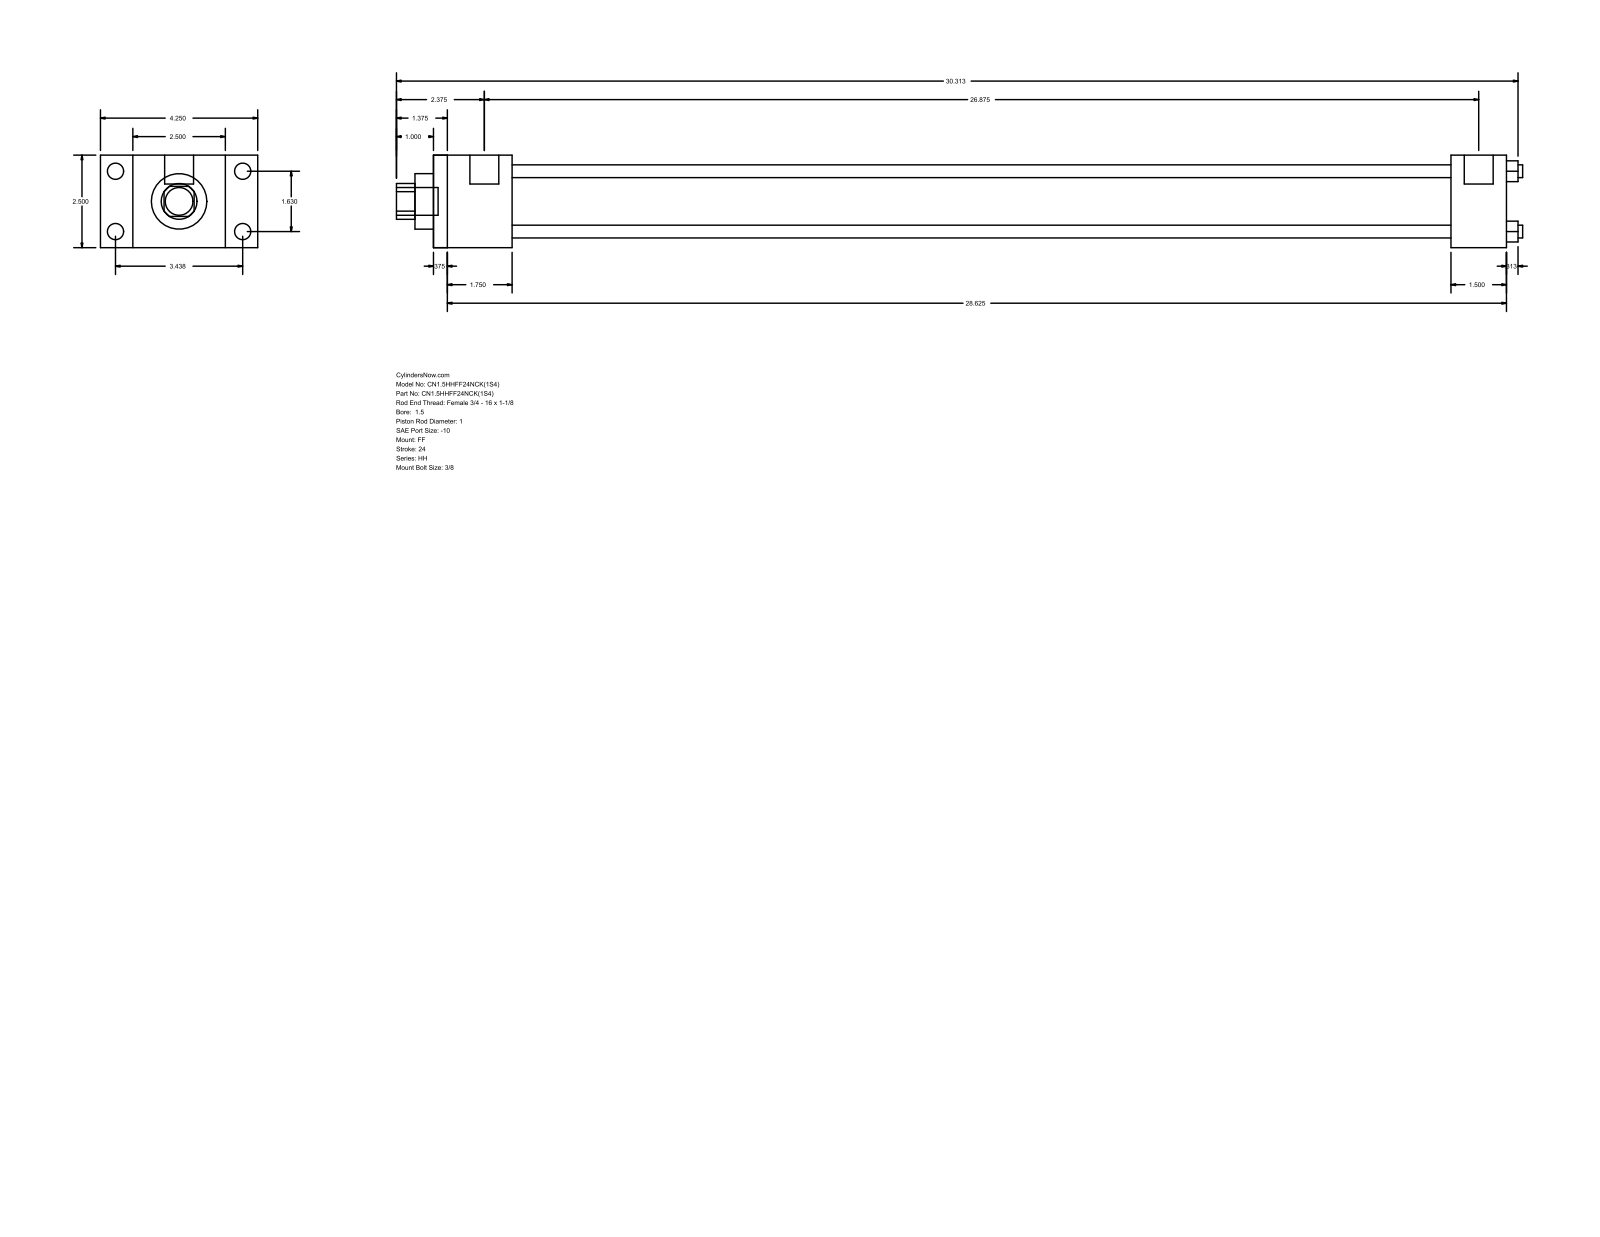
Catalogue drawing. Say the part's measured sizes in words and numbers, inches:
The part is named "HH_FF__0150_1". Its 3-D file was written by "GSSL Pune (CONFIG_CONTROL_DESIGN)". It is 0 solids with 92 faces: 64 planar, 28 cylindrical and 0 other. Overall it measures 30.437 by 4.25 by 2.5 inches. Round holes: 4 of diameter 0.345, 1 of diameter 1, 1 of diameter 1.5, 1 of diameter 1.75. Round bosses or shafts: 4 of diameter 0.438, 4 of diameter 0.219, 2 of diameter 0.781, 1 of diameter 0.75. Partial cylindrical surfaces (rounded edges, fillets, slot ends): 1 of radius 0.484. The main face-to-face distances are 2.5, 29, 0.375, 28.625, 2.125, 1.75, 26.875, 27.5, 27.125, 25.375. The hole center spacings are 1.152, 1.63, 2.305.
